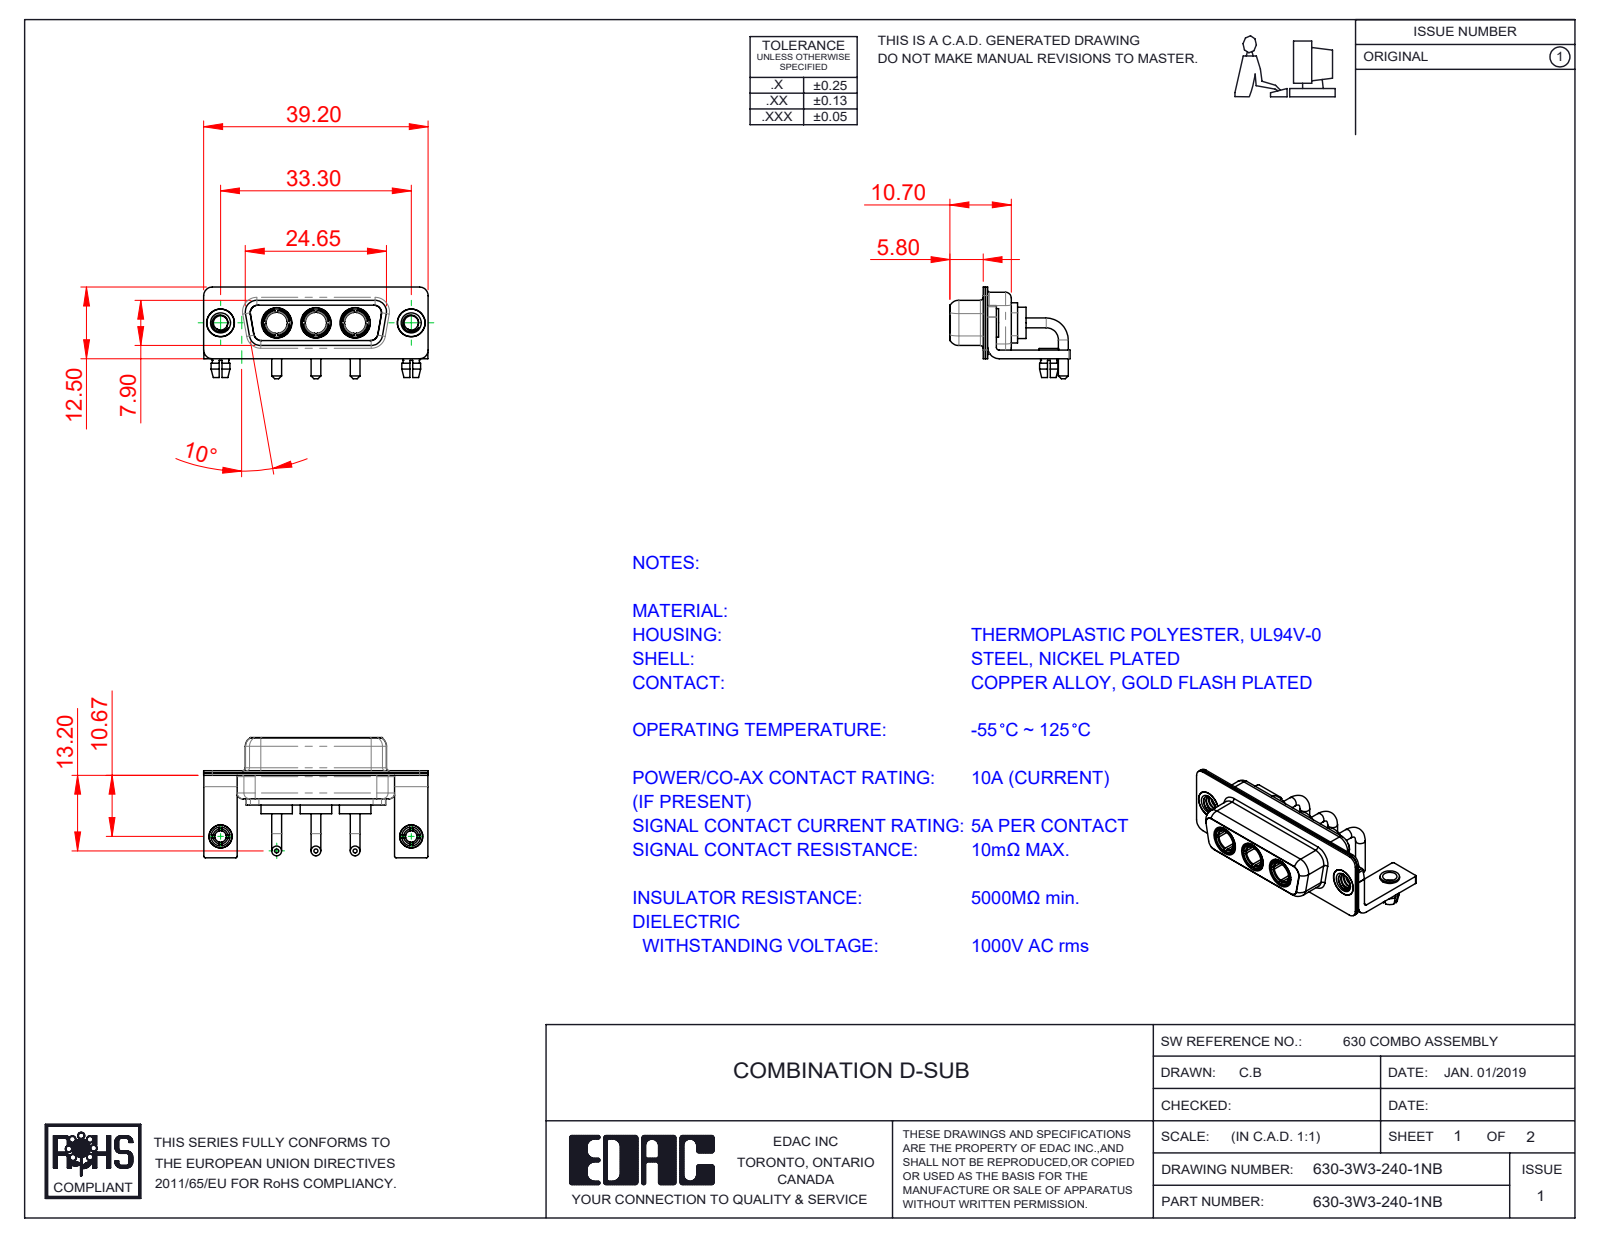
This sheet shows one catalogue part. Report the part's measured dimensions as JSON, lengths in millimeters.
{"part_name": "630Combo Shell Front_15 Contacts; 630Combo Stabilizer Bracket; 630Combo Housing_3W3; Power Socket_10A RA (+4 more)", "step_written_by": "SolidWorks 2020 (CONFIG_CONTROL_DESIGN)", "units": "millimeters", "bodies": {"solids": 15, "faces": 643, "planar": 222, "cylindrical": 262, "other": 159}, "overall_size": [39.2, 21, 16], "volume_mm3": 2767, "surface_area_mm2": 6571, "round_holes": [[4.85, 5], [2.5, 4], [3.7, 3], [5.3, 3], [2, 2], [3.2, 2], [4, 2], [4.05, 2]], "round_bosses_or_shafts": [[1.7, 6], [5.5, 3], [5.2, 3], [4.96, 3], [4.75, 3], [3.75, 3], [5, 2], [4.95, 2]], "partial_cylinders_radius": [[0.25, 16], [1.5, 16], [2, 13], [1.35, 12], [1.6, 8], [0.5, 5], [0.6, 4], [0.65, 4]], "face_to_face_distances": [0.4, 1.5, 0.8, 1.4, 0.45, 8.45, 1.8, 8.9, 5.2, 7.05], "hole_center_spacings": [6.85, 9.8, 16.65, 23.5, 33.3, 13.7]}
